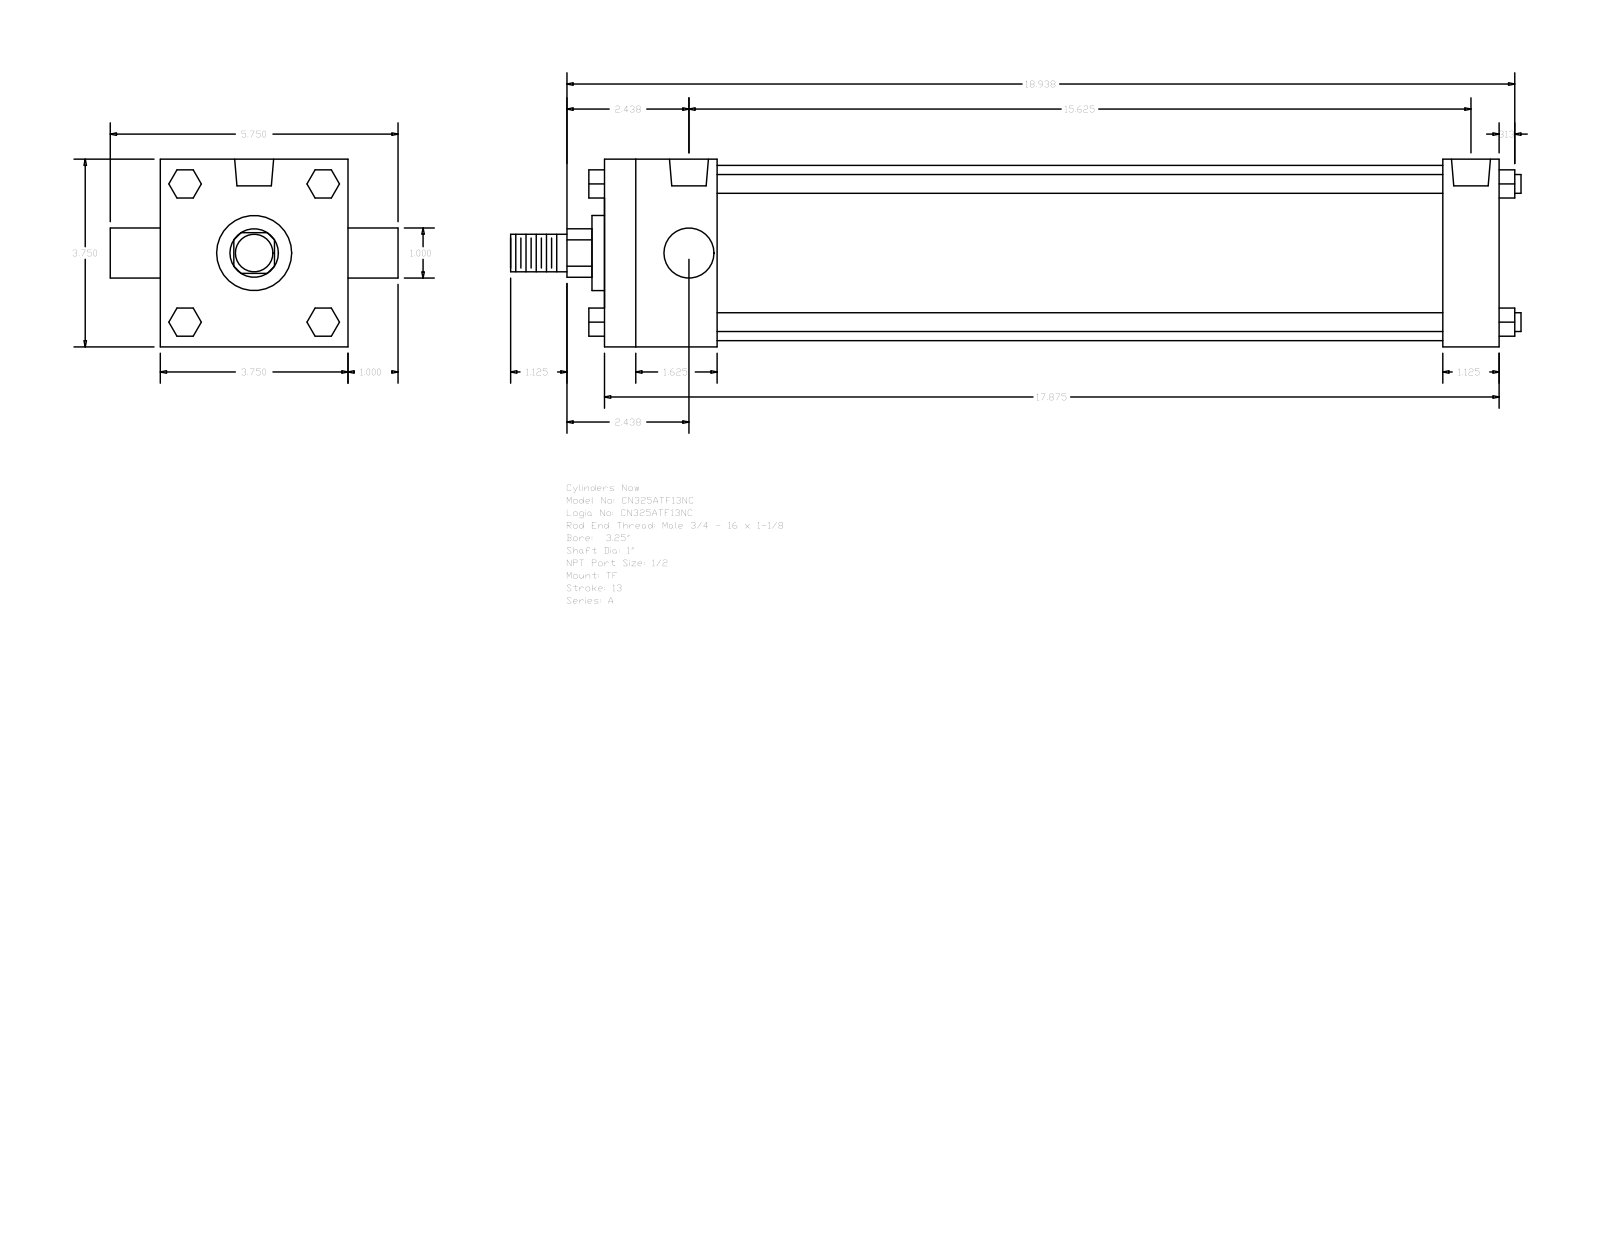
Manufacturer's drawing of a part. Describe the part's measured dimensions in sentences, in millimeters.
The part is named "A_TF__0325_1". Its 3-D file was written by "GSSL Pune (CONFIG_CONTROL_DESIGN)". It is 0 solids with 120 faces: 92 planar, 28 cylindrical and 0 other. Overall it measures 512.76 by 146.05 by 95.25 millimeters. Round holes: 3 of diameter 8.73, 2 of diameter 19.77. Round bosses or shafts: 4 of diameter 9.53, 2 of diameter 25.4, 1 of diameter 88.9, 1 of diameter 38.1, 1 of diameter 19.05. Partial cylindrical surfaces (rounded edges, fillets, slot ends): 1 of radius 12.29. The main face-to-face distances are 95.24, 454.02, 28.57, 57.15, 425.45, 368.3, 396.87, 14.28, 35.05, 60.71. The hole center spacings are 3.18, 393.7, 390.52, 396.88.
